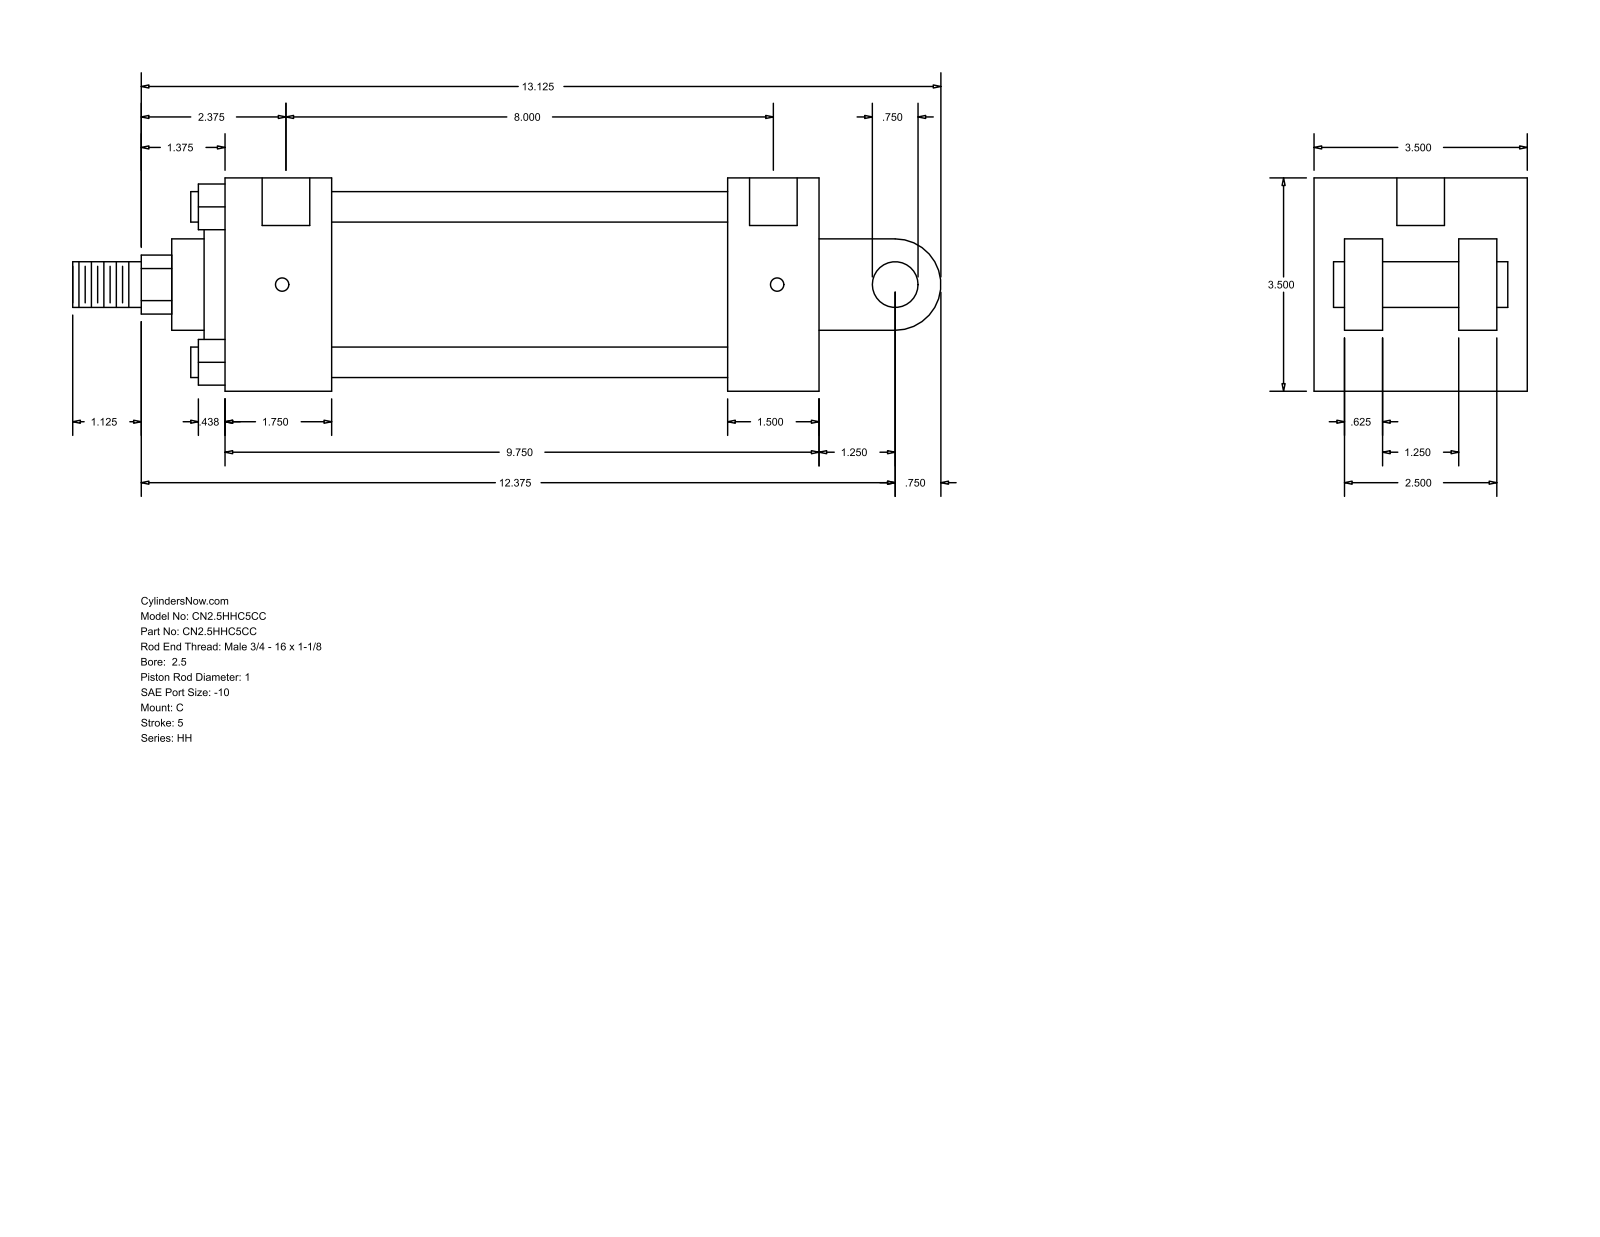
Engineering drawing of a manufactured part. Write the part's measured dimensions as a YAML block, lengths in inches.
part_name: "HH_C__0250_1"
step_written_by: "GSSL Pune (CONFIG_CONTROL_DESIGN)"
units: inches
bodies: {solids: 0, faces: 101, planar: 71, cylindrical: 30, other: 0}
overall_size: [14.25, 3.5, 3.5]
round_holes:
  - {diameter: 0.219, count: 4}
  - {diameter: 0.781, count: 2}
round_bosses_or_shafts:
  - {diameter: 0.5, count: 4}
  - {diameter: 0.75, count: 2}
  - {diameter: 2.875, count: 1}
  - {diameter: 2.375, count: 1}
  - {diameter: 1.5, count: 1}
  - {diameter: 1, count: 1}
partial_cylinders:
  - {radius: 0.484, count: 1}
  - {radius: 0.75, count: 1}
face_to_face_distances: [3.5, 1.5, 9.75, 2.5, 8.25, 1.75, 6.5, 8, 0.5, 1.125]
hole_center_spacings: [0.063, 8.062, 8.125, 8]
